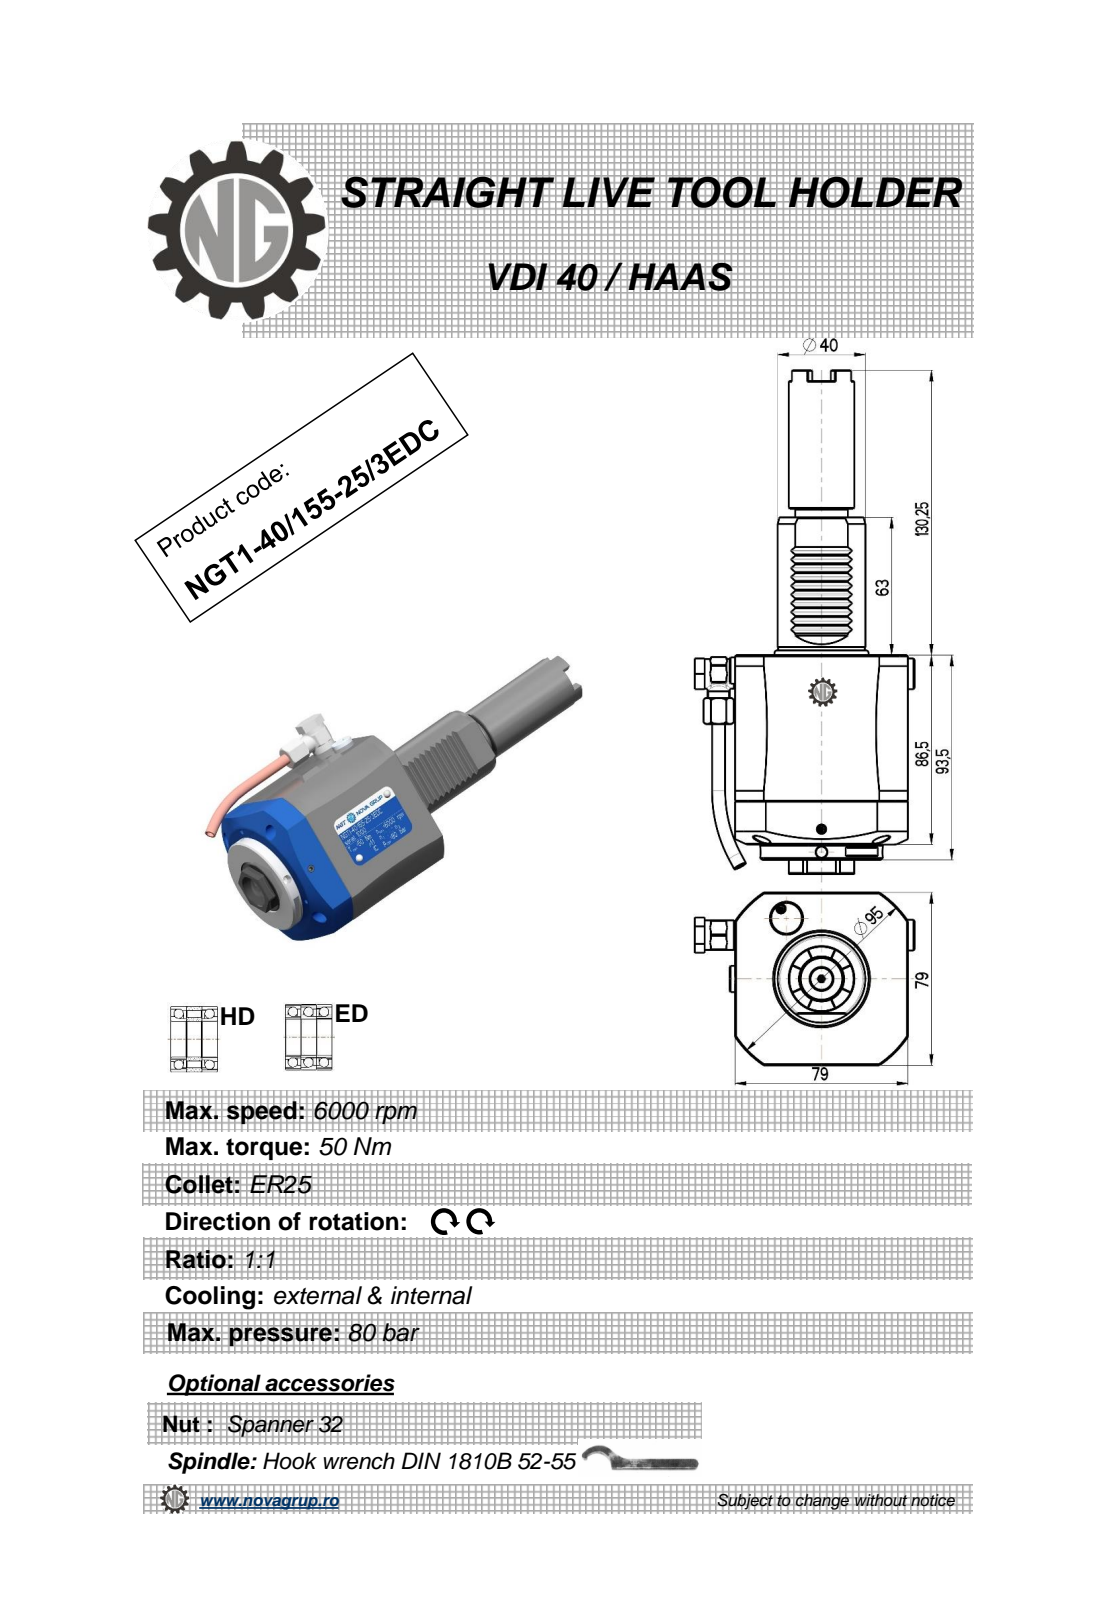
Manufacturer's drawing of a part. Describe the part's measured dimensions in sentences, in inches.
The part is named "NGT1_40_155_25_3HDC". Its 3-D file was written by "PRO/ENGINEER BY PARAMETRIC TECHNOLOGY CORPORATION, 2010280 (CONFIG_CONTROL_DESIGN)". It is 2 solids with 426 faces: 184 planar, 109 cylindrical and 133 other. Overall it measures 9.065 by 3.953 by 3.11 inches. Its volume is 39.12 cubic inches and its surface area 93.79 square inches. Round holes: 3 of diameter 0.157, 2 of diameter 0.197, 1 of diameter 0.118, 1 of diameter 0.236, 1 of diameter 0.244, 1 of diameter 0.354, 1 of diameter 0.394, 1 of diameter 0.433, 1 of diameter 0.709, 1 of diameter 0.787, 1 of diameter 1.043. Round bosses or shafts: 1 of diameter 2.205, 1 of diameter 1.575, 1 of diameter 1.181, 1 of diameter 0.945, 1 of diameter 0.551, 1 of diameter 0.535, 1 of diameter 0.512, 1 of diameter 0.472. Partial cylindrical surfaces (rounded edges, fillets, slot ends): 10 of radius 0.012, 6 of radius 0.016, 4 of radius 0.02, 1 of radius 0.303, 1 of radius 1.85, 1 of radius 1.87. The main face-to-face distances are 3.11, 3.406, 0.276, 3.681, 0.111, 6.161, 5.886, 2.48, 0.334, 0.557. The hole center spacings are 0.016, 2.011, 2.026, 3.304.
